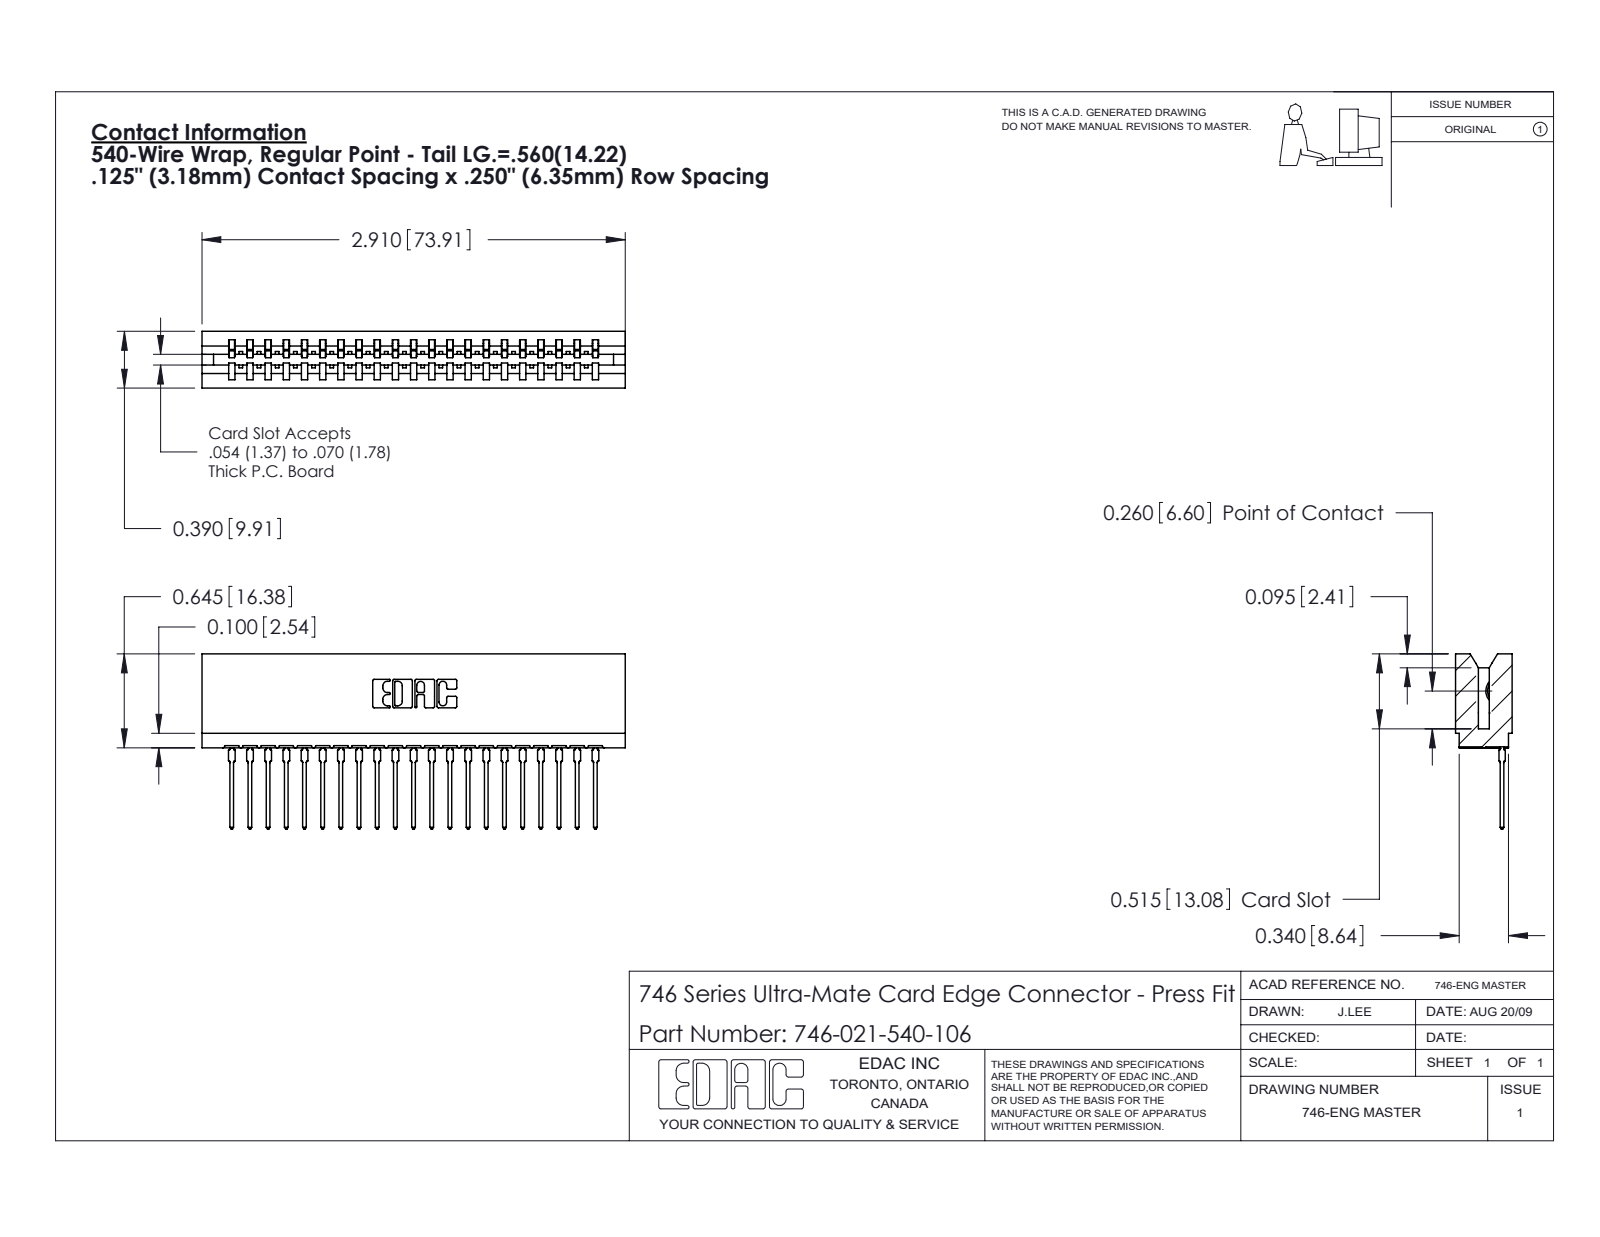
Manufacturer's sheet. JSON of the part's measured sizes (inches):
{"part_name": "746-292-001_540; 746-021-540-106; 746 Part_.515 Slot Depth - 06", "step_written_by": "SolidWorks 2020 (CONFIG_CONTROL_DESIGN)", "units": "inches", "bodies": {"solids": 22, "faces": 2366, "planar": 1379, "cylindrical": 441, "other": 546}, "overall_size": [2.91, 1.204, 0.39], "volume_in3": 0.482, "surface_area_in2": 18.01, "partial_cylinders_radius": [[0.021, 42], [0.01, 22], [0.015, 22], [0.007, 6], [0.031, 6], [0.005, 4], [0.011, 4], [0.026, 3]], "face_to_face_distances": [0.057, 0.333, 0.25, 0.39, 0.5, 0.025, 0.307, 0.083, 0.042, 0.125]}
